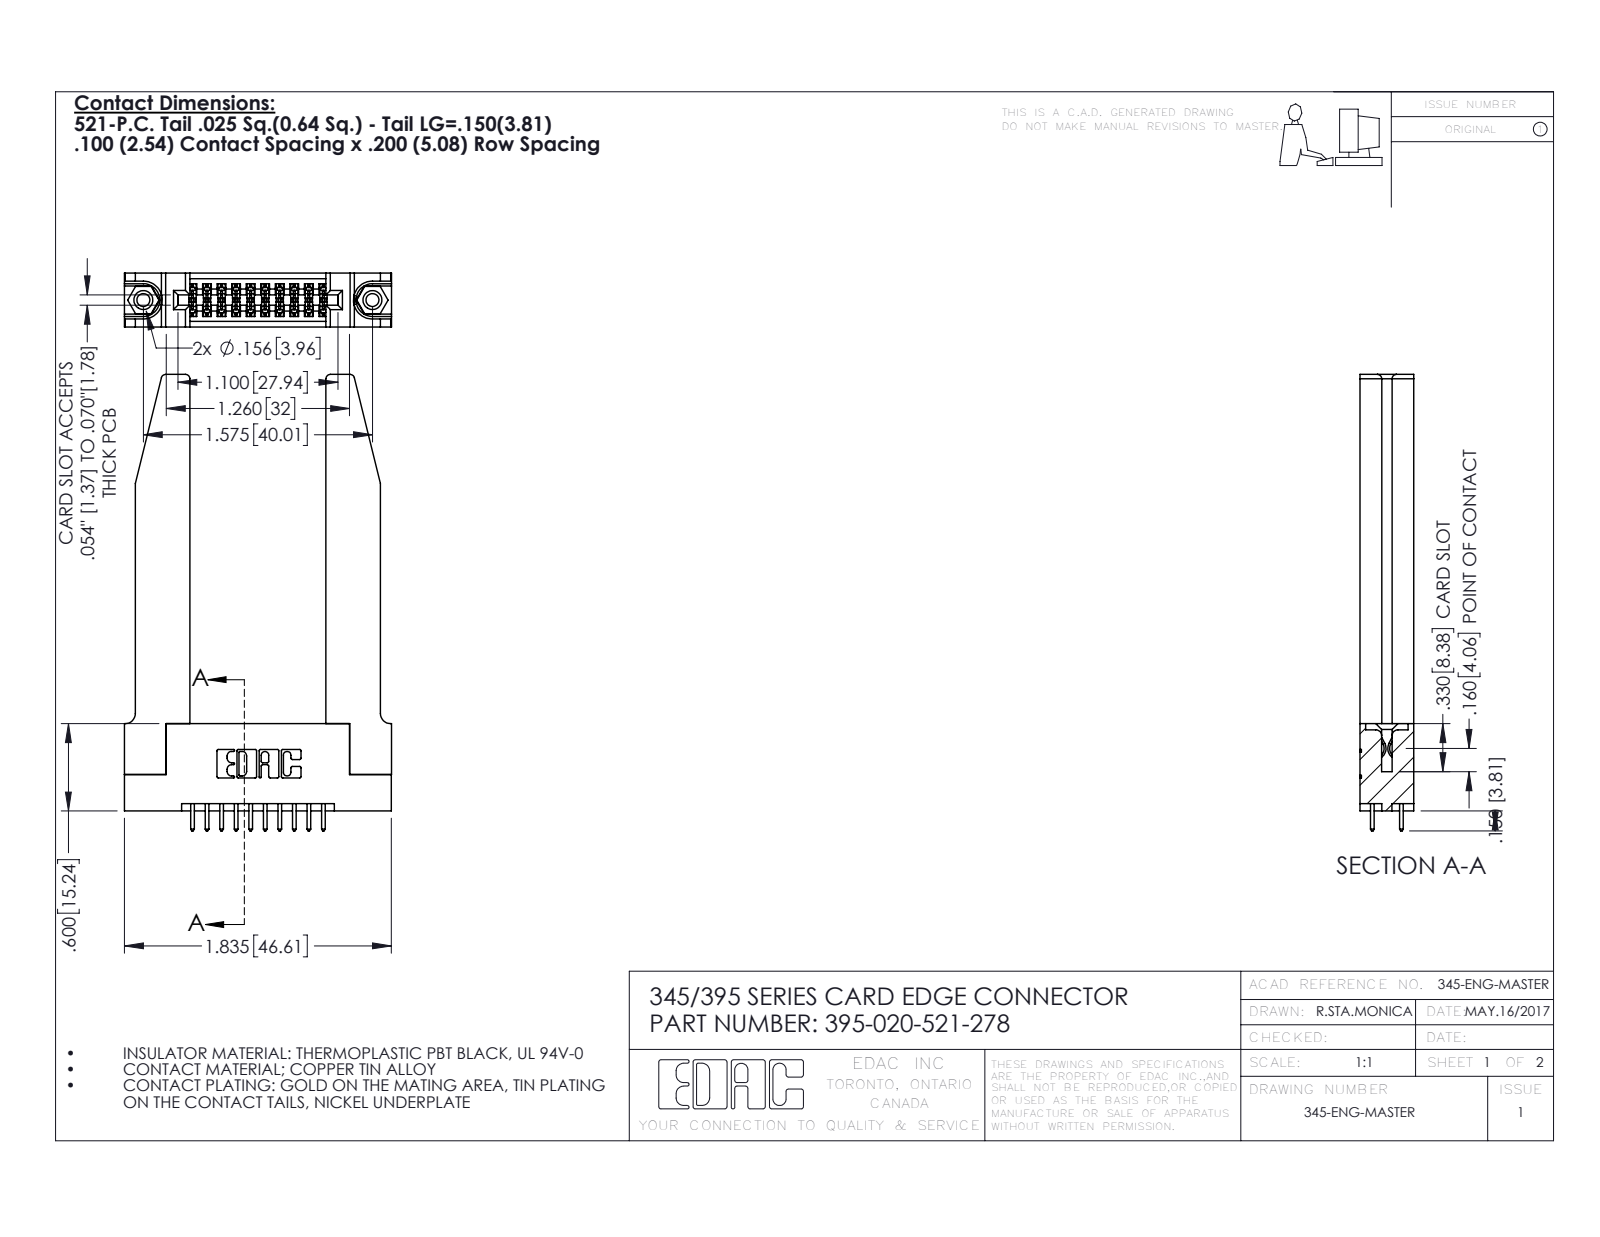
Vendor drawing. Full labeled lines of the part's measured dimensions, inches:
Part name (STEP PRODUCT): 395-020-521-278; 345-292-001_345-293-121; 345-250-001_345-250-001-102; 345-220-078_345-220-078 (+1 more)
STEP written by: SolidWorks 2016 (CONFIG_CONTROL_DESIGN)
Units: inches
Bodies: 25 solids, 1360 faces (882 planar, 426 cylindrical, 52 other)
Overall size (bounding box): 3.137 × 1.836 × 0.37
Volume: 0.732 in³ · Surface area: 19.24 in²
Round holes (diameter × count): ⌀0.089 ×2, ⌀0.125 ×2, ⌀0.156 ×2, ⌀0.064 ×1
Round bosses / shafts (diameter × count): ⌀0.155 ×2
Partial cylindrical surfaces — rounded edges, fillets, slot ends (radius × count): R0.006 ×30, R0.01 ×22, R0.01 ×20, R0.03 ×8, R0.007 ×6, R0.031 ×6, R0.026 ×3, R0.014 ×2
Main face-to-face distances: 0.37, 0.072, 0.298, 0.2, 0.148, 0.15, 0.077, 0.22, 0.935, 0.098
Hole centre spacings: 0.27, 1.344, 1.575
